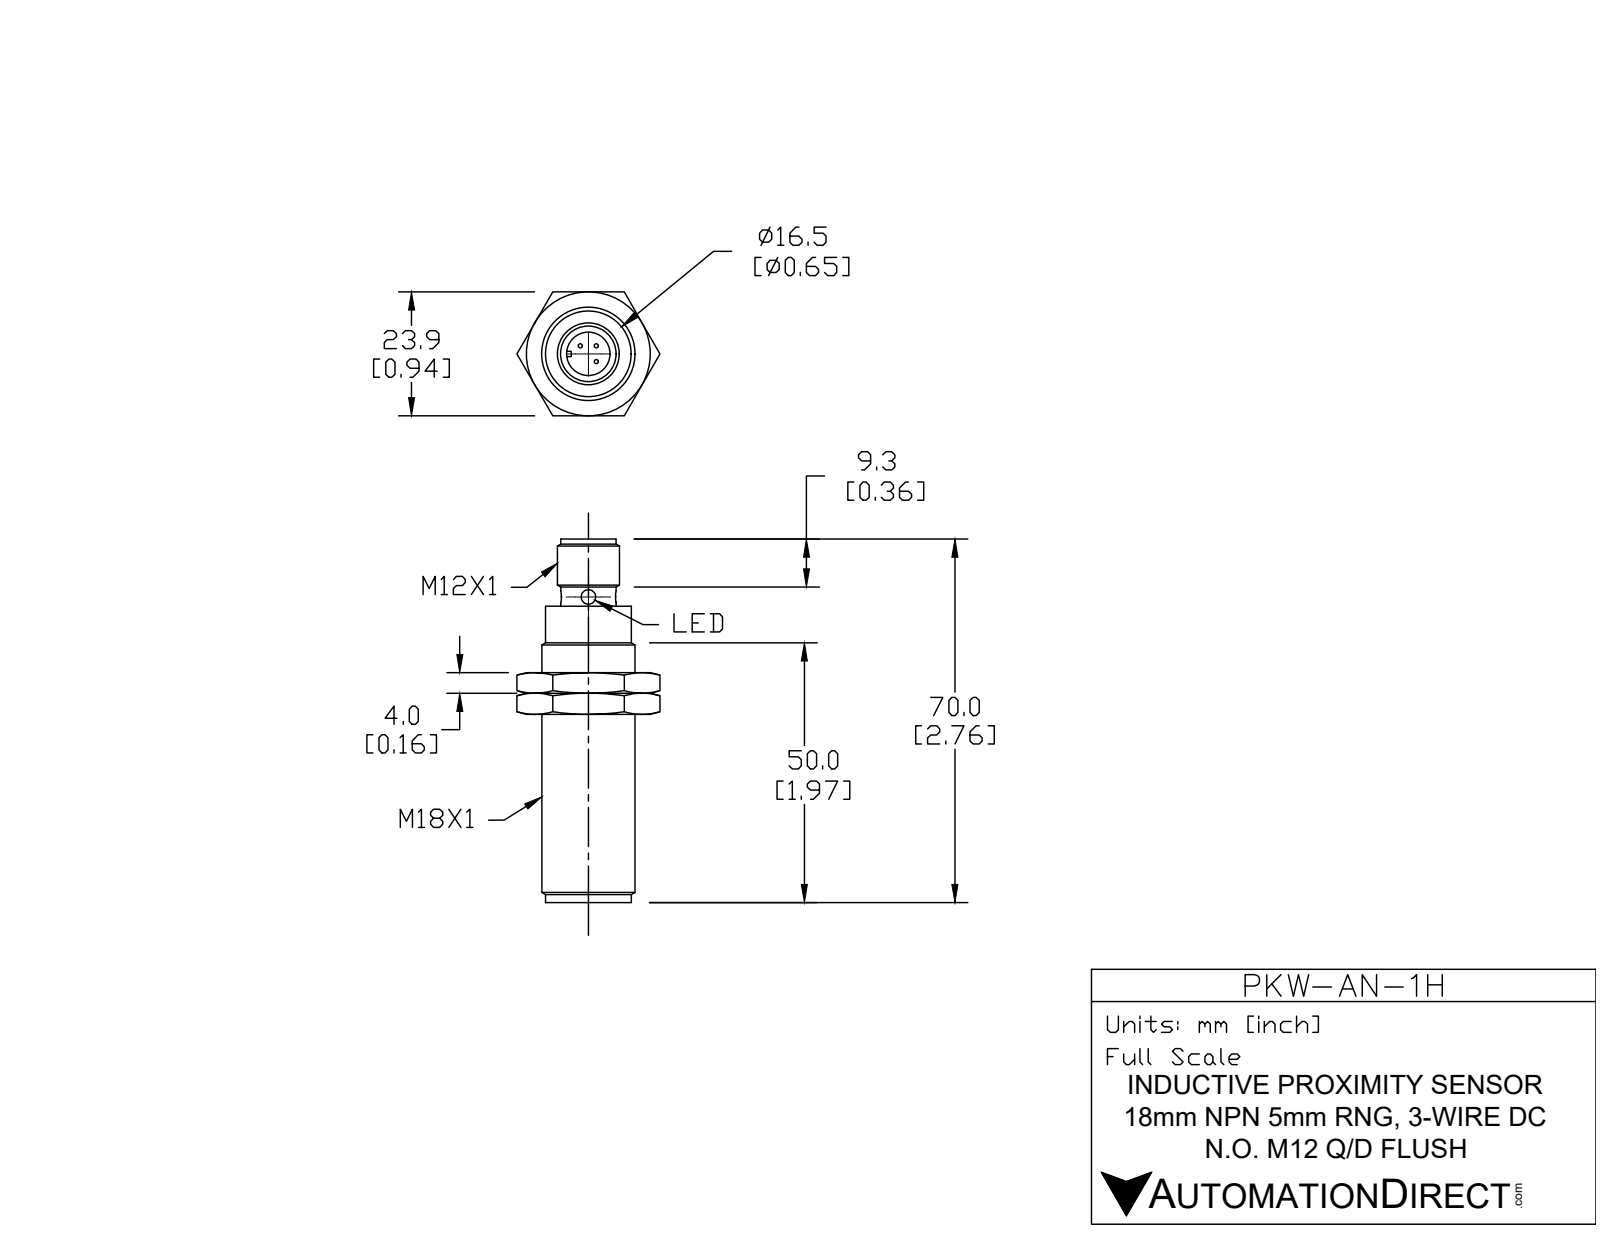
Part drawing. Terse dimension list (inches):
name: PKW-AN-1H
written by: SolidWorks 2017 (AUTOMOTIVE_DESIGN)
unit: in
bodies: 3 solids, 91 faces (22 planar, 29 cylindrical, 40 other)
size: 2.756 × 1.091 × 0.945
volume: 1.055 in³; area: 10.03 in²
holes: 2× ⌀0.098, 1× ⌀0.331, 1× ⌀0.666
bosses: 1× ⌀0.709, 1× ⌀0.669, 1× ⌀0.472, 1× ⌀0.453, 1× ⌀0.433
rounds: 1× R0.024, 1× R0.177
face distances: 0.157, 0.945, 1.181, 1.024, 0.315, 1.339, 0.906, 1.063, 1.22, 2.244
